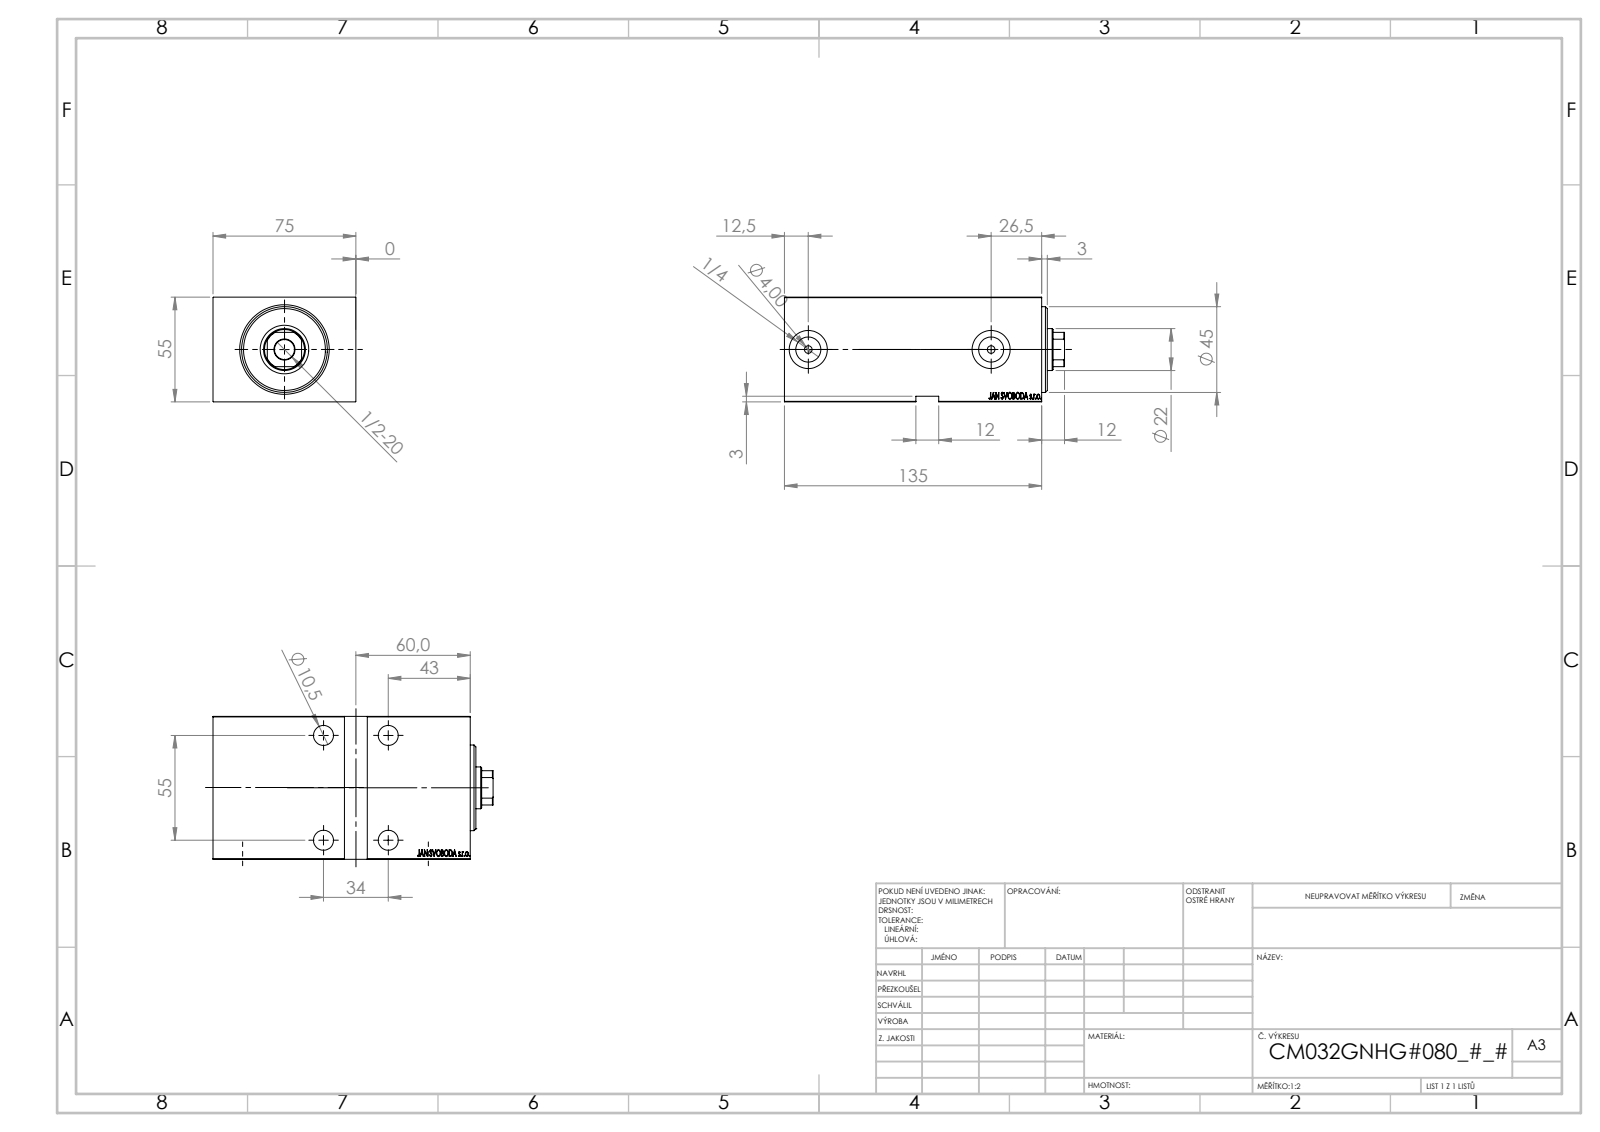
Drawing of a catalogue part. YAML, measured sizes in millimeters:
part_name: "V450CM_VC_G; V450CM_G_VCP; Zatka_OIL_PORT; V450CM_G_Body"
step_written_by: "SolidWorks 2019 (CONFIG_CONTROL_DESIGN)"
units: millimeters
bodies: {solids: 5, faces: 894, planar: 440, cylindrical: 56, other: 398}
overall_size: [147, 75, 55]
volume: 495099
surface_area: 84937
round_holes:
  - {diameter: 10.5, count: 5}
  - {diameter: 16.5, count: 4}
  - {diameter: 4, count: 2}
  - {diameter: 13.16, count: 2}
  - {diameter: 20, count: 2}
  - {diameter: 22, count: 1}
  - {diameter: 25.5, count: 1}
  - {diameter: 32, count: 1}
  - {diameter: 34, count: 1}
  - {diameter: 45, count: 1}
round_bosses_or_shafts:
  - {diameter: 18, count: 2}
  - {diameter: 27, count: 1}
partial_cylinders:
  - {radius: 10.5, count: 1}
face_to_face_distances: [55, 75, 135, 5, 3, 130, 125, 10, 120, 138]
hole_center_spacings: [34, 55, 64.66, 96]
